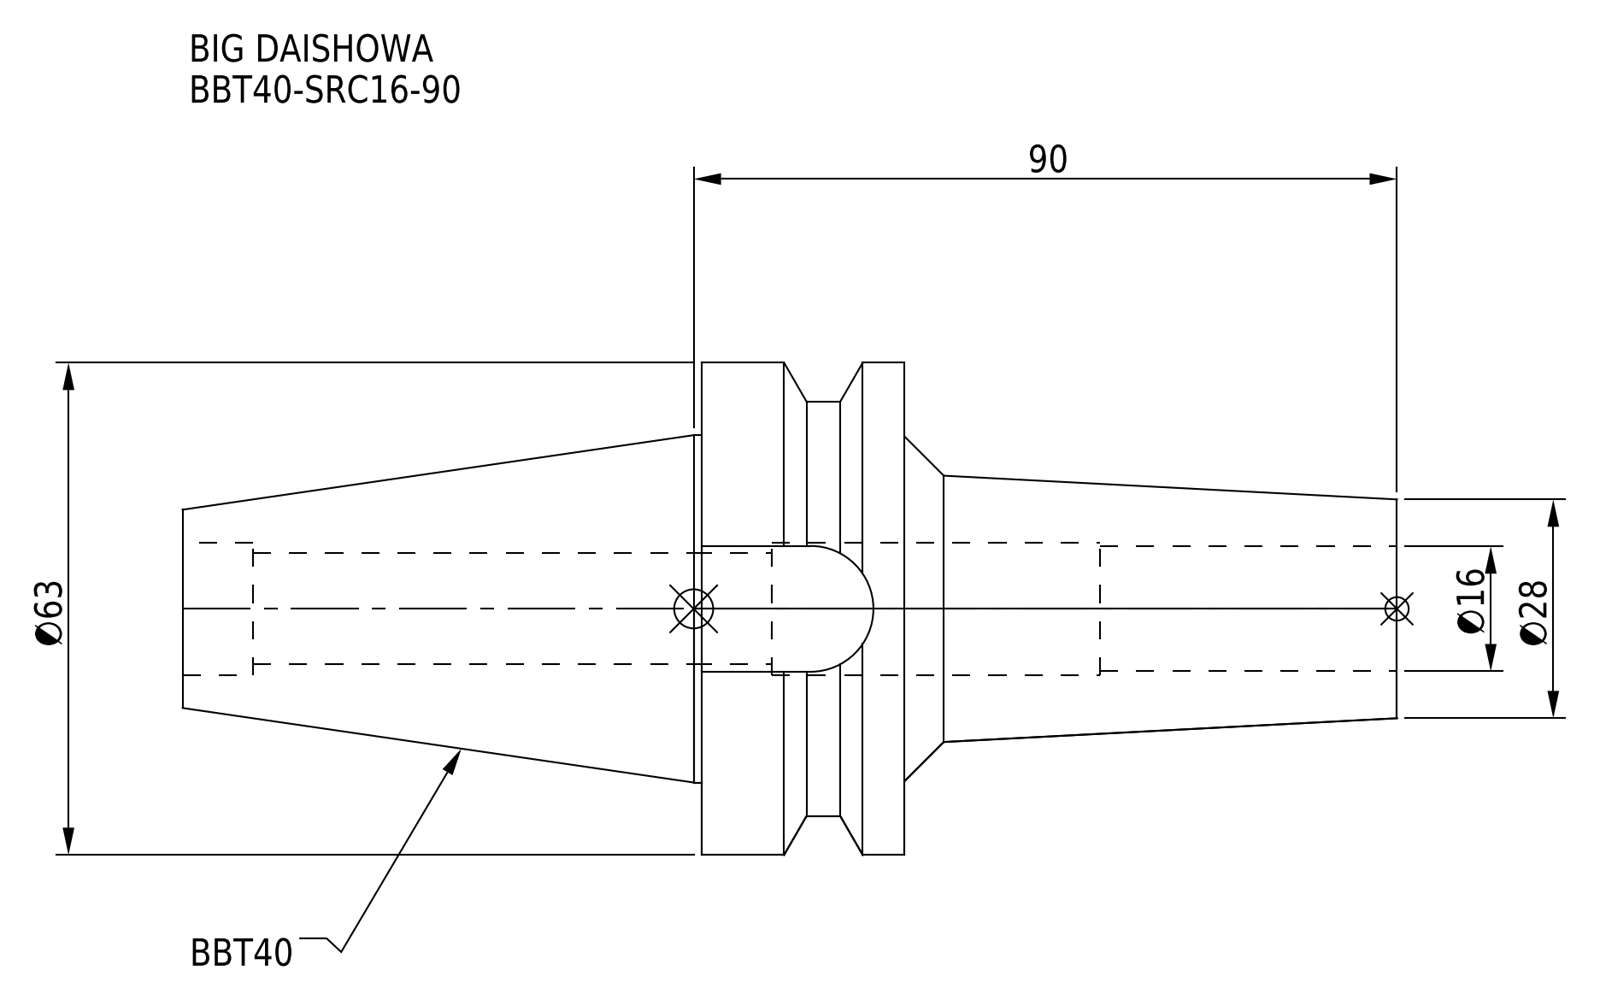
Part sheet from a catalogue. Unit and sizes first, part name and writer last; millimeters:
Units: millimetres
Overall size (bounding box): 155.4 × 63 × 63
Round holes (diameter × count): ⌀14.2 ×1, ⌀16 ×1, ⌀17 ×1
Round bosses / shafts (diameter × count): ⌀63 ×1, ⌀53 ×1, ⌀44.45 ×1
Partial cylindrical surfaces — rounded edges, fillets, slot ends (radius × count): R8.05 ×1
Main face-to-face distances: 26, 63, 89, 66.4, 45, 155.4, 92.4, 16.1, 9, 80
Volume: 155 906 mm³ · Surface area: 31 764 mm²
Bodies: 1 solid, 43 faces (13 planar, 20 cylindrical, 10 other)
Part name (STEP PRODUCT): BBT40-SRC16-90
STEP written by: CREO PARAMETRIC BY PTC INC, 2016380 (AUTOMOTIVE_DESIGN)
